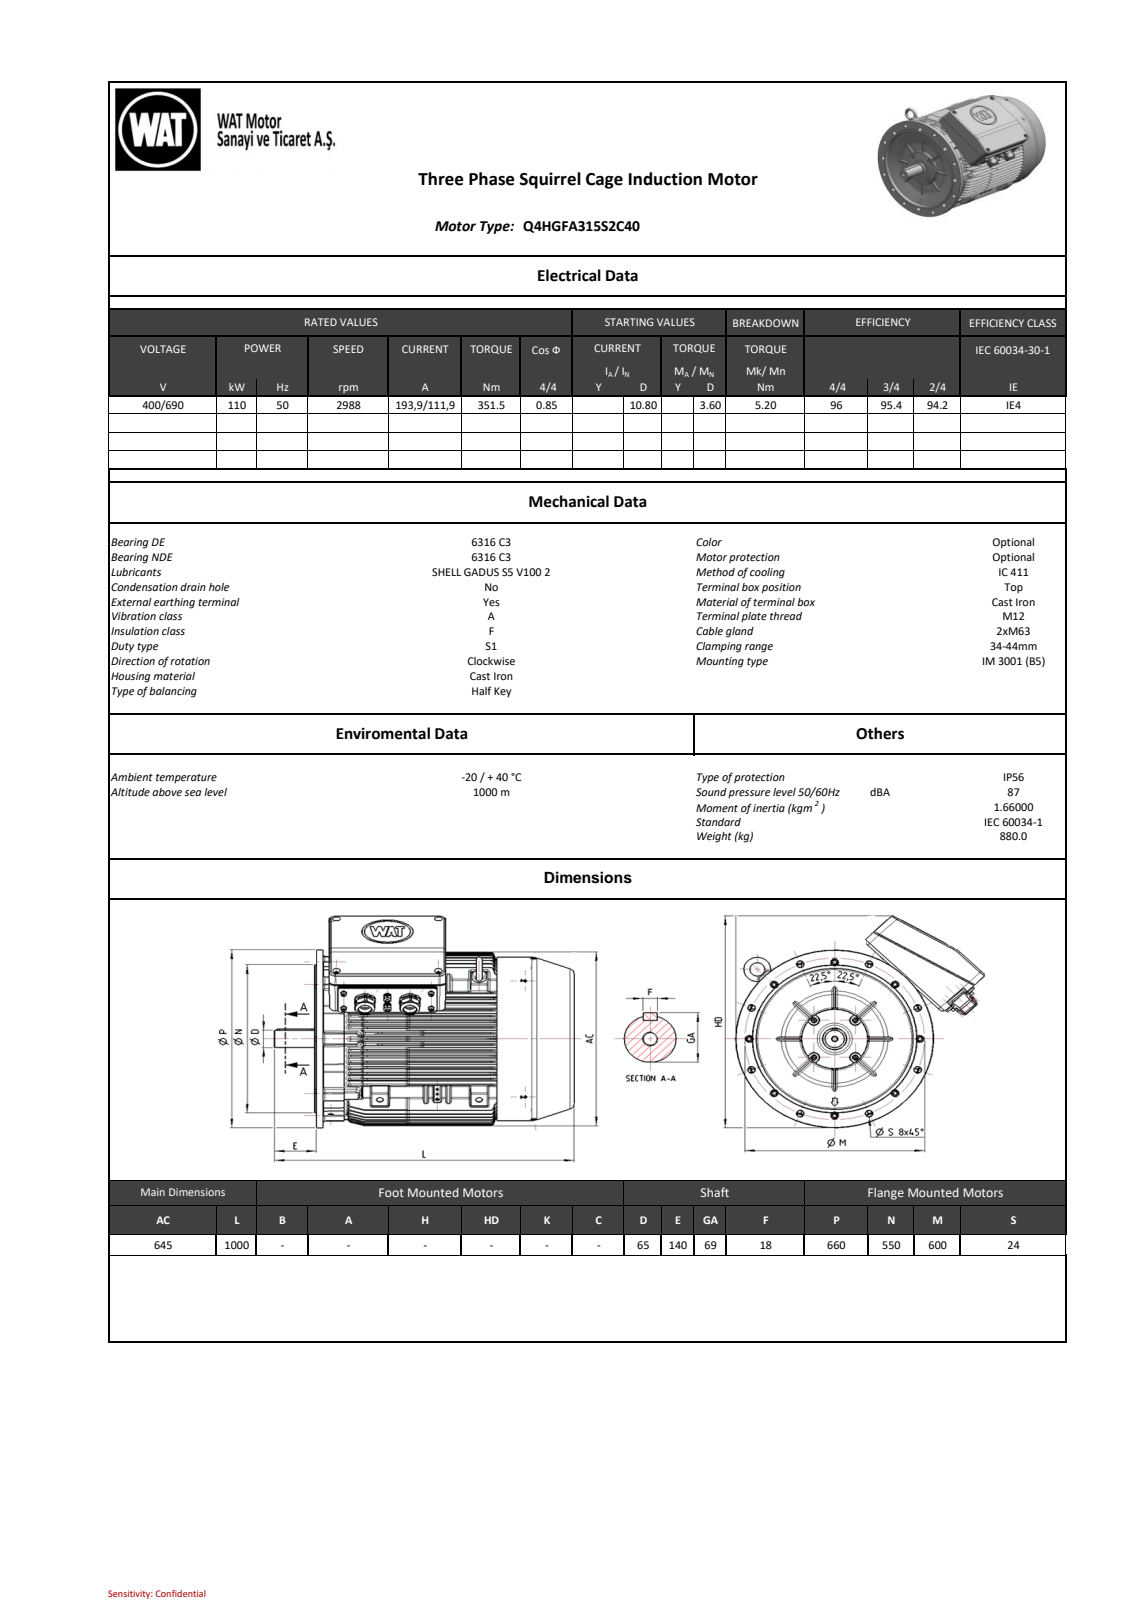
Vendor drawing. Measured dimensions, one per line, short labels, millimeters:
name: 26009910674F4pg8
written by: SIEMENS PLM Software NX 11.0 (AUTOMOTIVE_DESIGN)
unit: mm
bodies: 0 solids, 6630 faces (3439 planar, 1195 cylindrical, 1996 other)
size: 1000 × 829.19 × 785.69
holes: 8× ⌀24, 8× ⌀26, 6× ⌀8, 5× ⌀8.5, 5× ⌀20, 4× ⌀22, 3× ⌀9, 2× ⌀4, 2× ⌀10.3, 2× ⌀11, 2× ⌀12, 2× ⌀12.1
bosses: 8× ⌀16, 8× ⌀10, 6× ⌀20, 4× ⌀5, 2× ⌀64.8, 2× ⌀50, 1× ⌀660, 1× ⌀607
rounds: 469× R6, 149× R3, 66× R2.09, 61× R2.61, 35× R0.8, 26× R10, 19× R0.4, 15× R1.5
face distances: 117, 305.15, 20.71, 743, 62.4, 41.51, 284.35, 20.8, 263.64, 1.5
hole spacings: 486.48, 79.06, 115.07, 115.08, 213.21, 218.13, 226.79, 277.7
